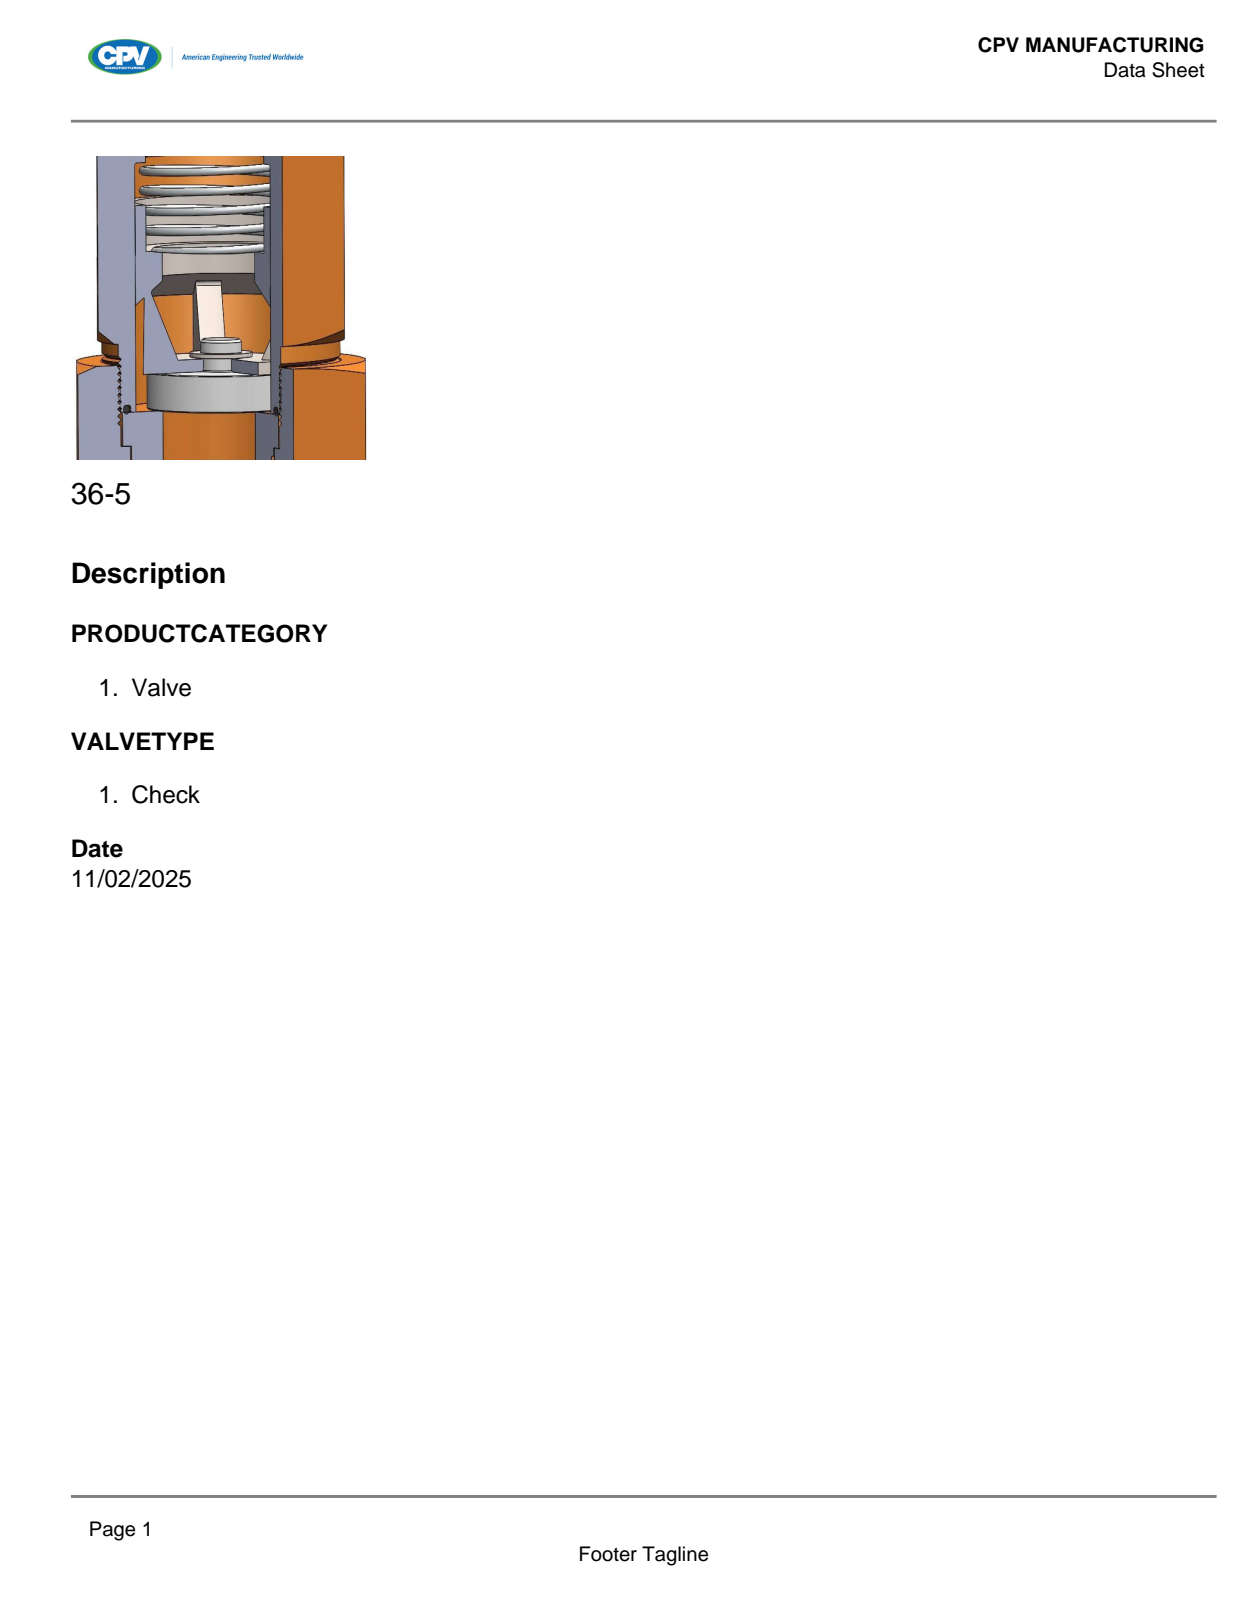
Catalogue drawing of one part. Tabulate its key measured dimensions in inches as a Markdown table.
| quantity | value |
| --- | --- |
| part name | 36-5 |
| STEP written by | SolidWorks 2018 (AUTOMOTIVE_DESIGN) |
| units | inches |
| bodies | 1 solid, 108 faces (28 planar, 39 cylindrical, 41 other) |
| overall size | 4.718 × 3.245 × 2.81 |
| volume | 19.03 in³ |
| surface area | 60.83 in² |
| round holes (diameter × count) | 1 × 1 |
| round bosses / shafts (diameter × count) | 2.245 × 1, 2 × 1 |
| partial cylindrical surfaces (radius × count) | 0.95 × 1 |
| main face-to-face distances | 0.215, 2.595, 2.38, 2.81, 0.515, 2.295, 0.3, 2.08, 1, 1.78 |
